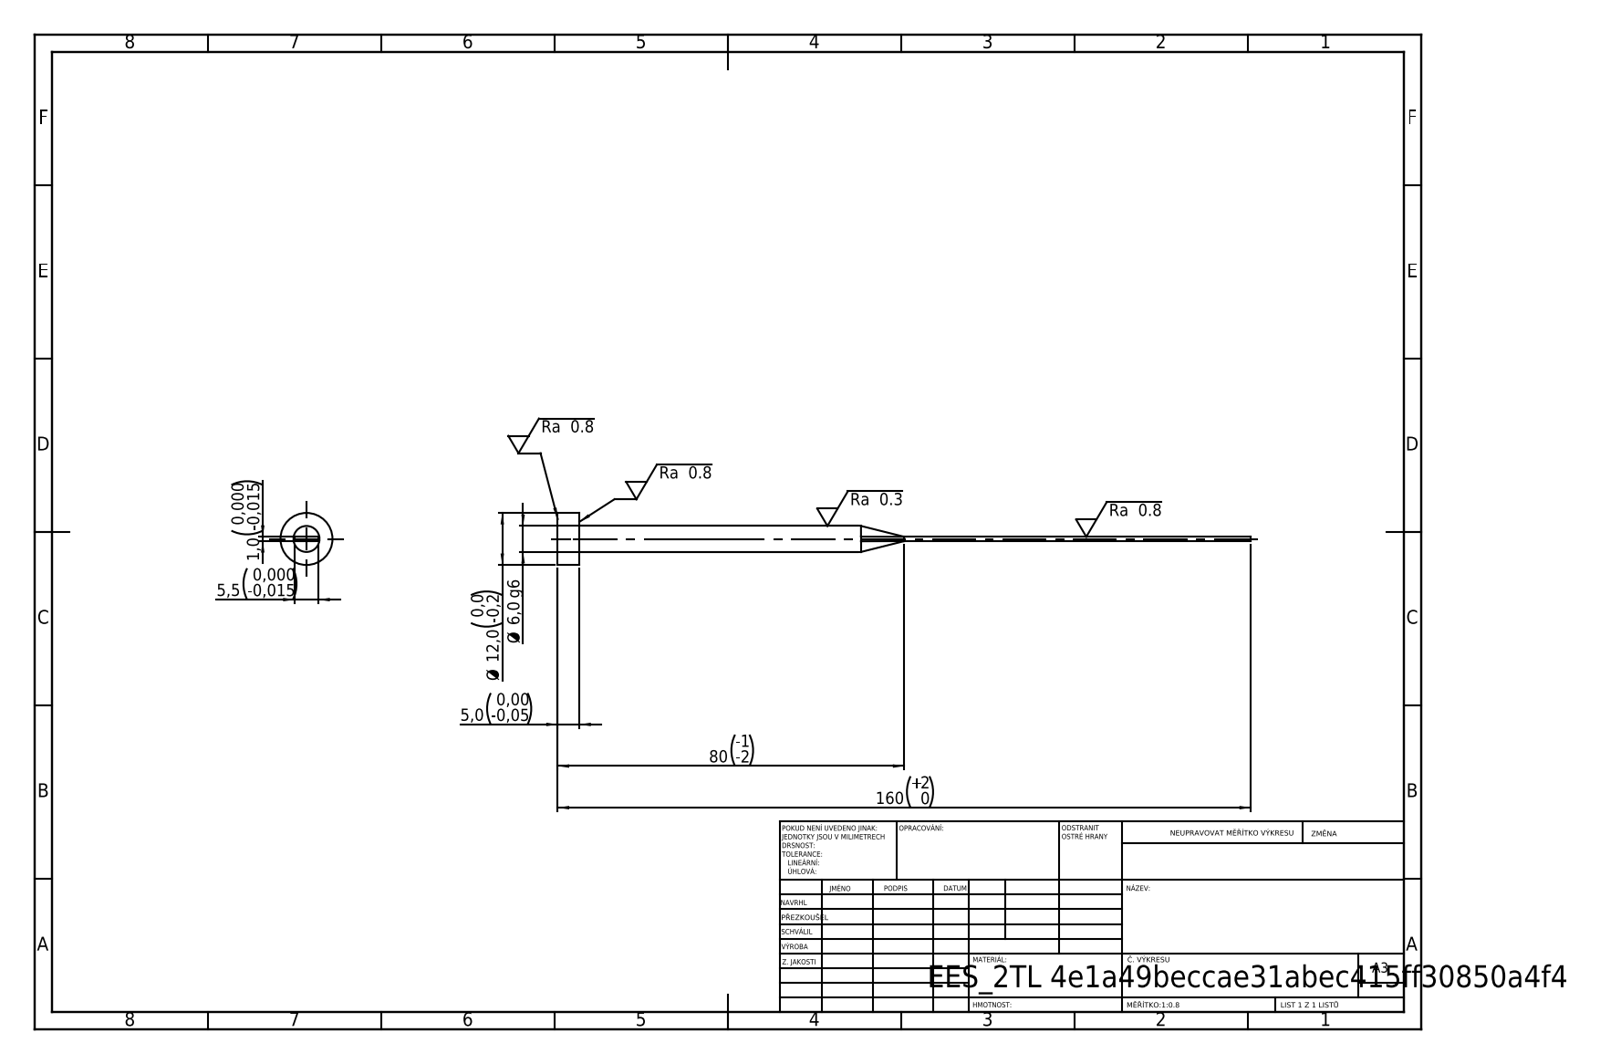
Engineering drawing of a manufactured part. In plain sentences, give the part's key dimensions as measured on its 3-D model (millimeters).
Its 3-D file was written by "SolidWorks 2019 (CONFIG_CONTROL_DESIGN)". It is 1 solid with 15 faces: 7 planar, 4 cylindrical and 4 other. Overall it measures 160 by 12 by 12 millimeters. Its volume is 3 002 cubic millimeters and its surface area 2 811 square millimeters. Round bosses or shafts: 1 of diameter 12, 1 of diameter 6. The main face-to-face distances are 1, 5, 5.5, 160, 155.
